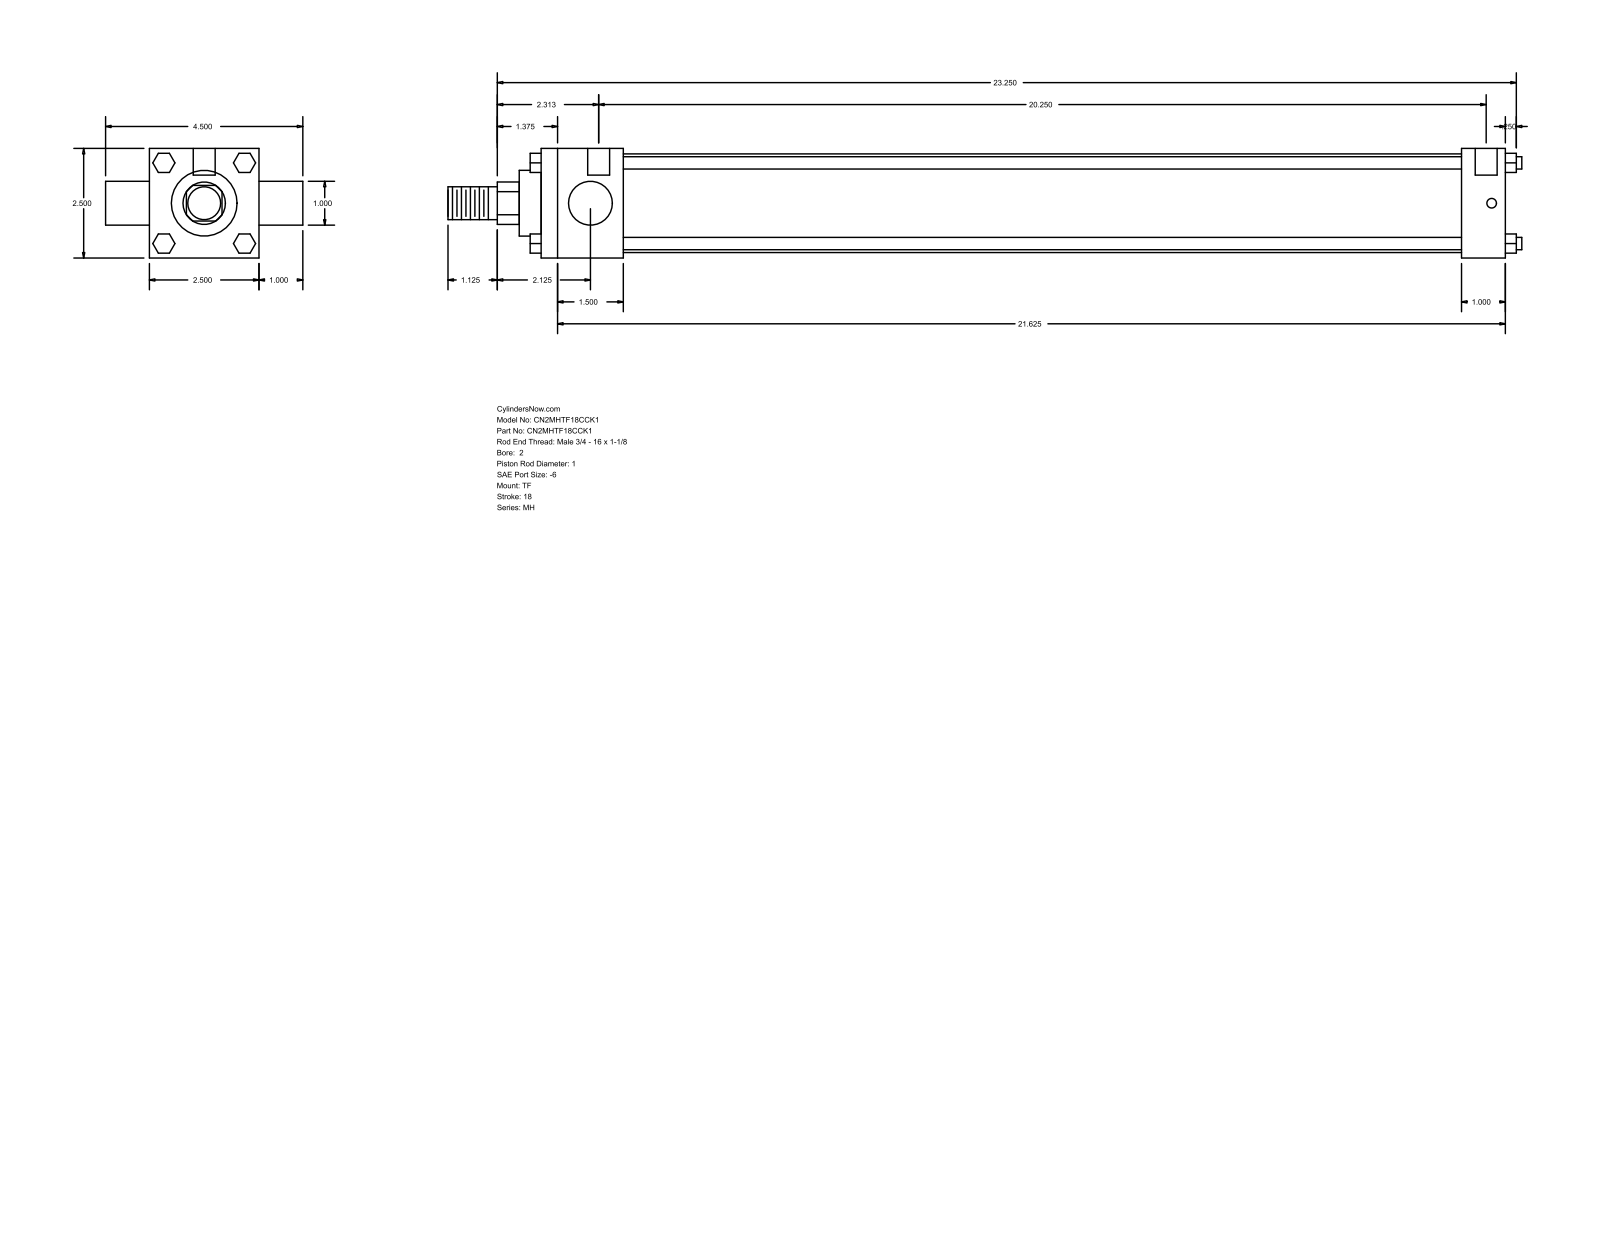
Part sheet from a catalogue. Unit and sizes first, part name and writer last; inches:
Units: inches
Overall size (bounding box): 24.5 × 4.5 × 2.5
Round holes (diameter × count): ⌀0.219 ×3, ⌀0.5 ×2
Round bosses / shafts (diameter × count): ⌀0.281 ×4, ⌀1 ×2, ⌀2.25 ×1, ⌀1.5 ×1, ⌀0.75 ×1
Partial cylindrical surfaces — rounded edges, fillets, slot ends (radius × count): R0.484 ×1
Main face-to-face distances: 2.5, 22, 1, 1.875, 21, 19.125, 20.125, 3.5, 22.5, 0.25
Hole centre spacings: 0.125, 0.187, 20.25, 20.375, 20.437, 20.562
Bodies: 0 solids, 120 faces (92 planar, 28 cylindrical, 0 other)
Part name (STEP PRODUCT): MH_TF__0200_1
STEP written by: GSSL Pune (CONFIG_CONTROL_DESIGN)
